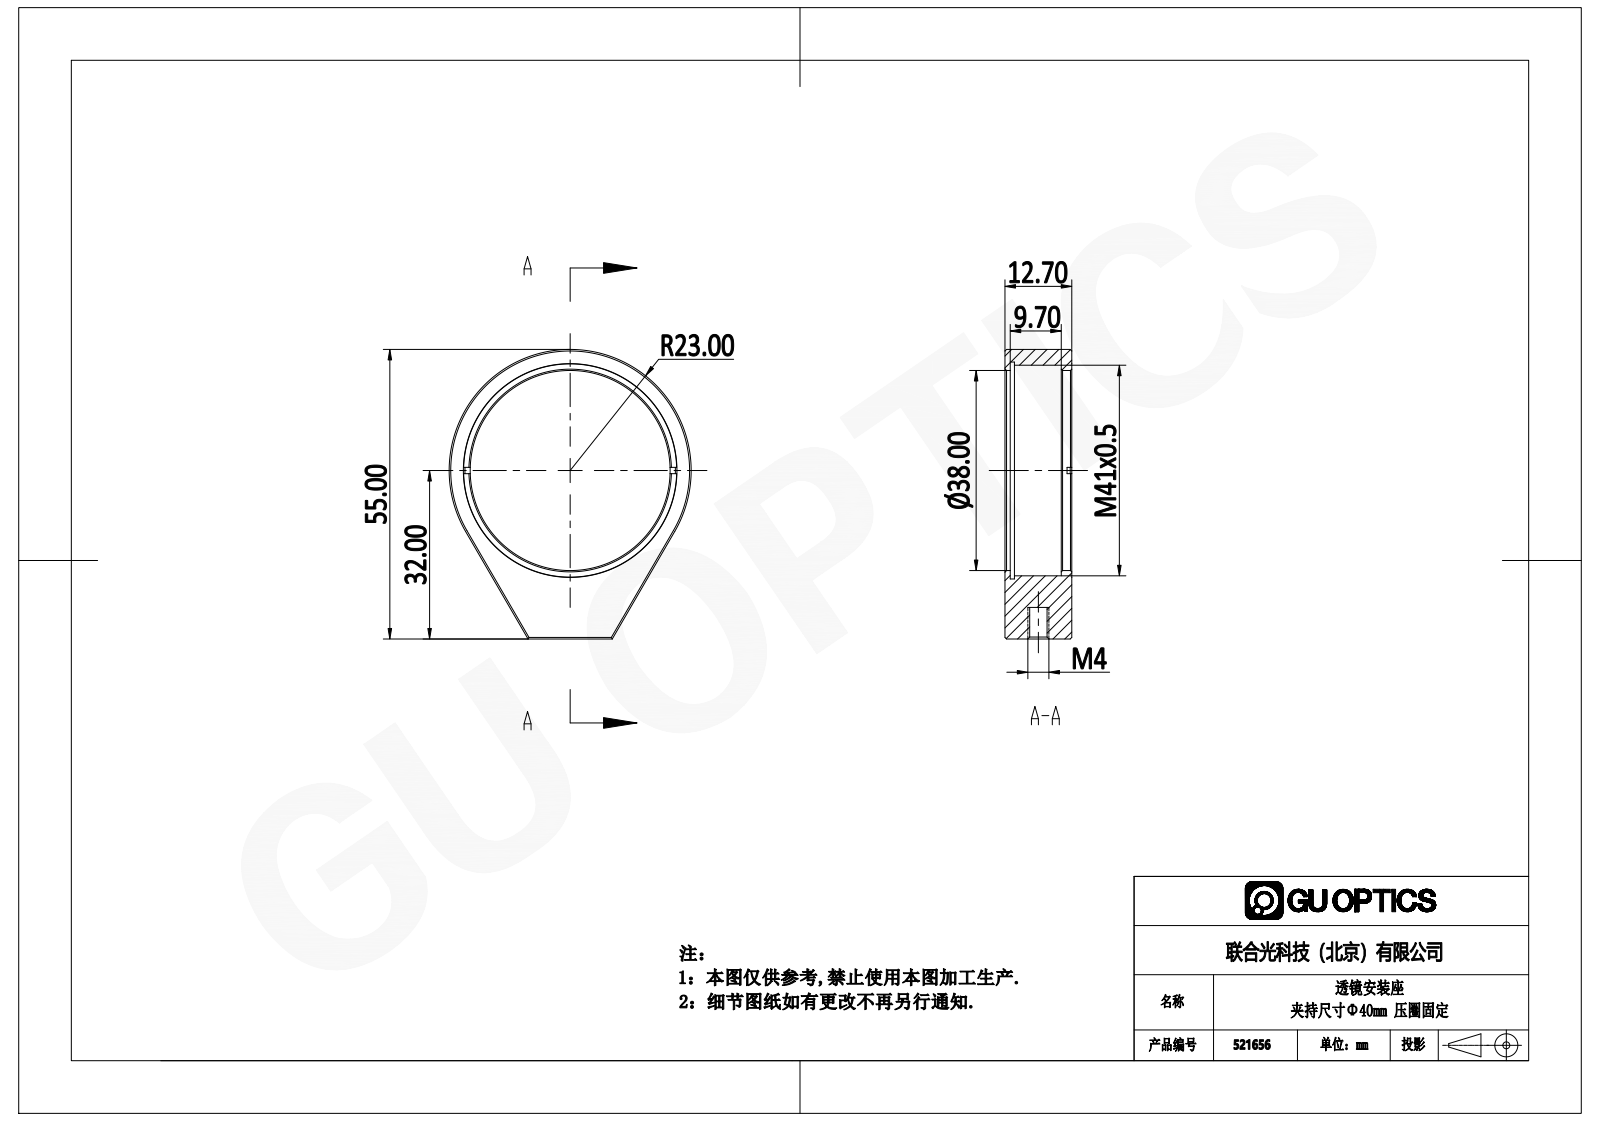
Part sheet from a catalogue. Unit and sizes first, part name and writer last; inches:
Units: inches
Overall size (bounding box): 2.165 × 1.811 × 0.5
Round holes (diameter × count): ⌀0.13 ×1, ⌀1.496 ×1, ⌀1.575 ×1, ⌀1.622 ×1
Partial cylindrical surfaces — rounded edges, fillets, slot ends (radius × count): R0.906 ×1
Main face-to-face distances: 0.5, 0.039, 0.461, 0.421, 0.382, 0.079, 0.071, 0.031, 0.35, 0.429
Bodies: 0 solids, 53 faces (22 planar, 13 cylindrical, 18 other)
Part name (STEP PRODUCT): 1.3.1.36_ZZT-M40
STEP written by: SolidWorks 2021 (CONFIG_CONTROL_DESIGN)
